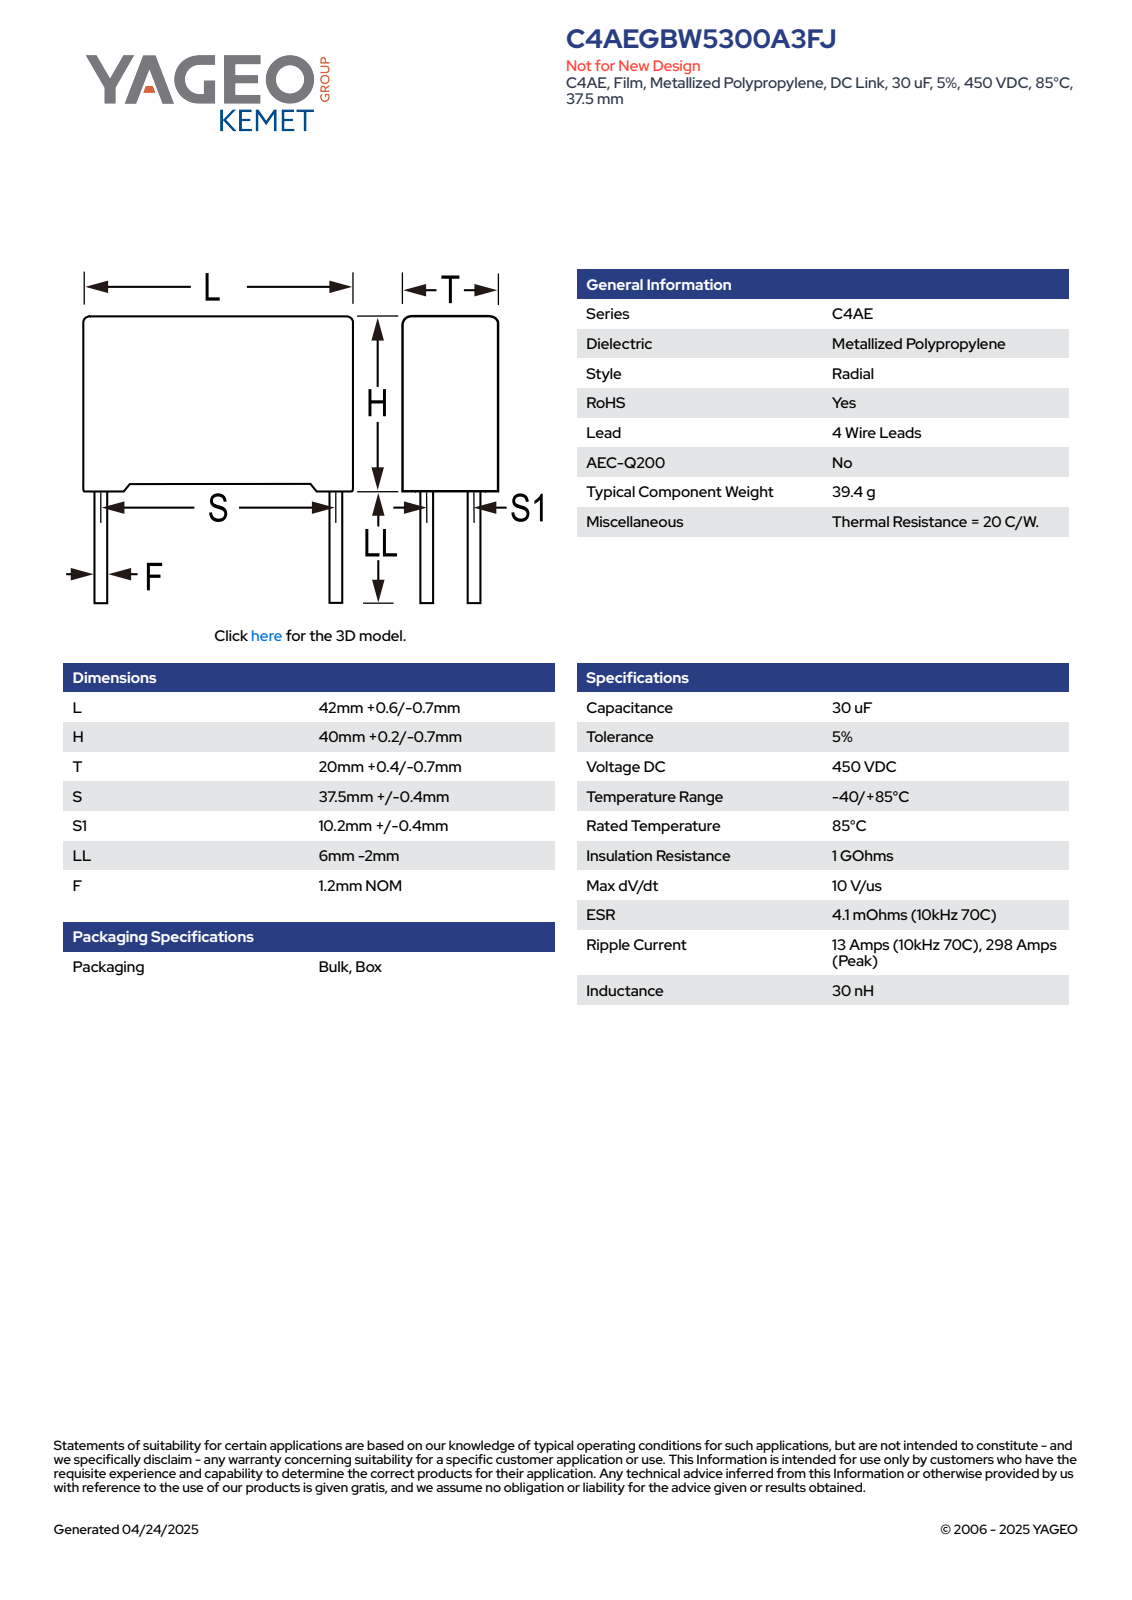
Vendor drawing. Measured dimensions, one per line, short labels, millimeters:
name: CFP_RB4_42X40X20_L42.6H40.2T20.4S37.5S110.2LL4F1.2
written by: SolidWorks 2014 (AUTOMOTIVE_DESIGN)
unit: mm
bodies: 4 solids, 87 faces (79 planar, 8 cylindrical, 0 other)
size: 44.2 × 42.6 × 20.41
volume: 34 029 mm³; area: 7 007 mm²
bosses: 4× ⌀1.2
face distances: 20.4, 42.6, 39.02, 1.18, 40.2, 1.25, 20.41, 41.35, 19.15, 40.1
